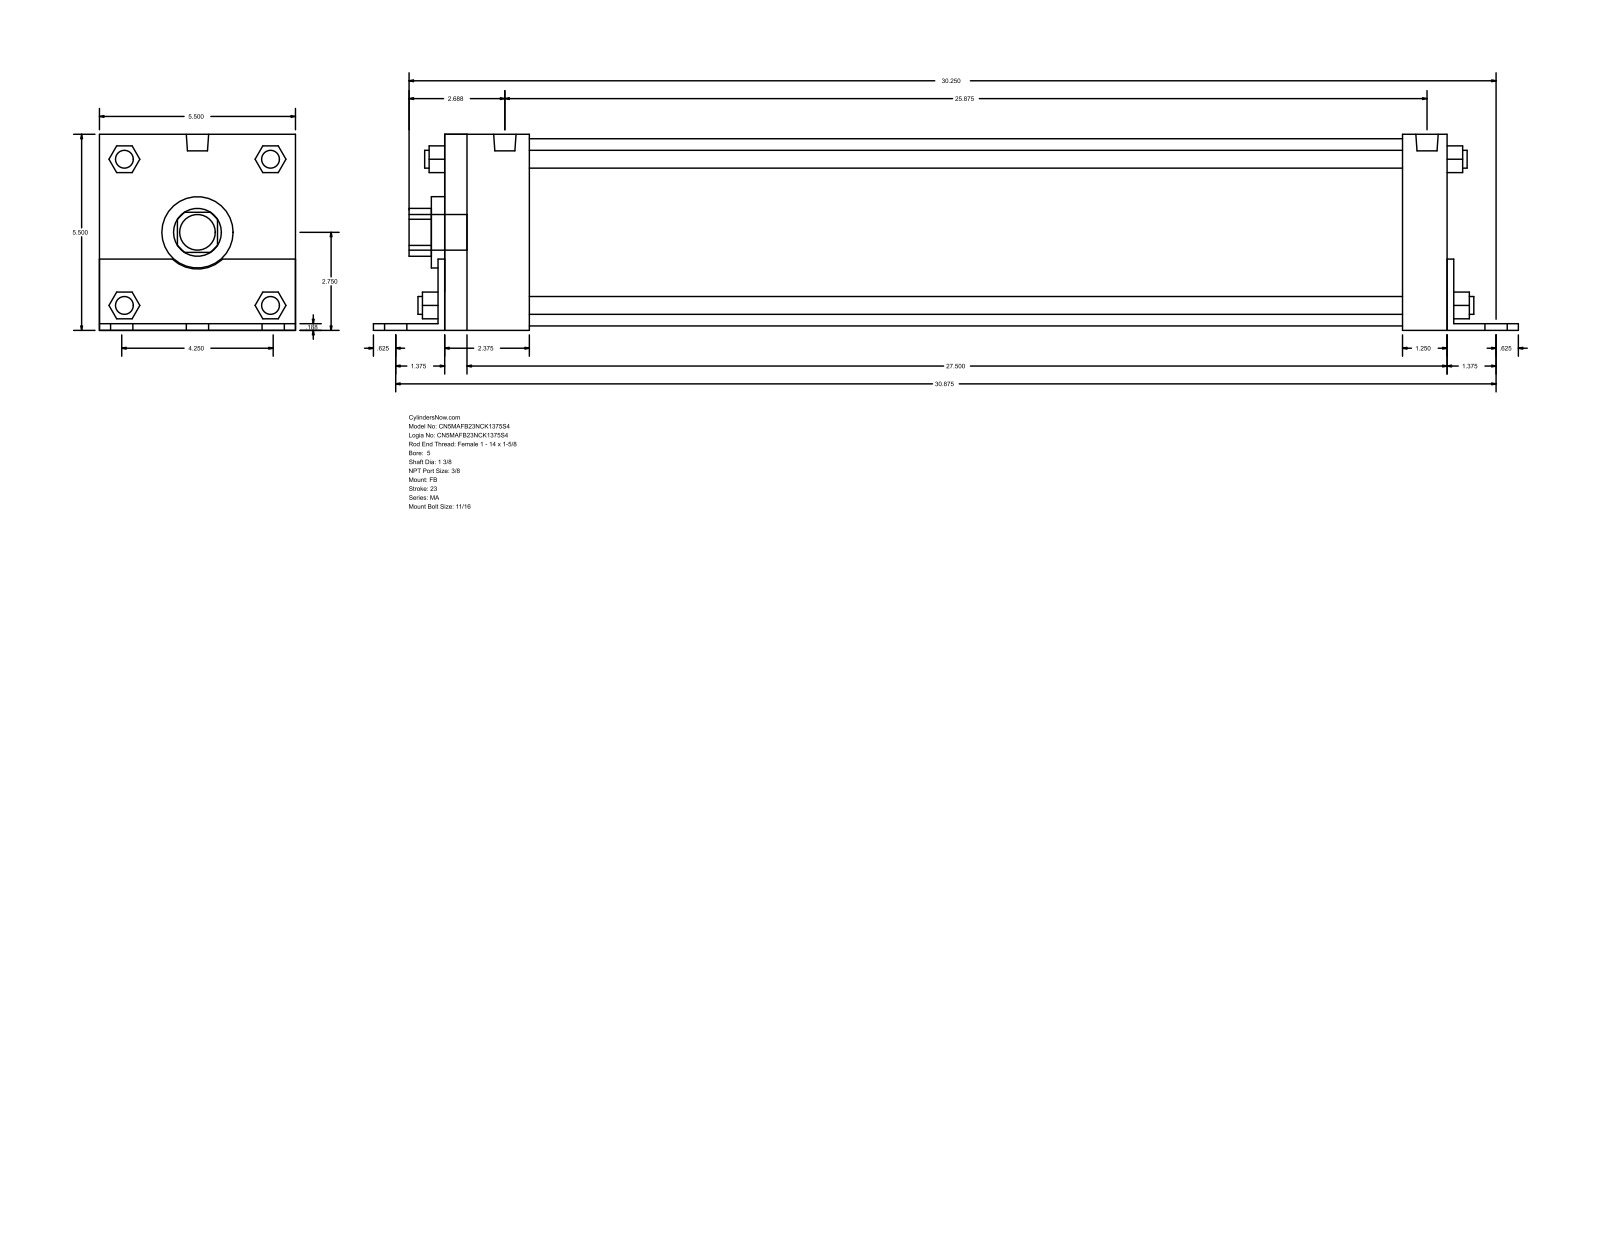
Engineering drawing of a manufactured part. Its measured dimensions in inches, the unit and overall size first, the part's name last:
Units: inches
Overall size (bounding box): 32.125 × 5.502 × 5.5
Round holes (diameter × count): ⌀1.375 ×1, ⌀2 ×1, ⌀5.25 ×1
Round bosses / shafts (diameter × count): ⌀0.687 ×6, ⌀0.5 ×4, ⌀0.437 ×4, ⌀0.627 ×2, ⌀1 ×1
Partial cylindrical surfaces — rounded edges, fillets, slot ends (radius × count): R0.672 ×1, R1.03 ×1
Main face-to-face distances: 5.5, 0.187, 5.502, 0.185, 5.315, 28.125, 0.188, 28.313, 28.312, 28.5
Bodies: 0 solids, 140 faces (105 planar, 35 cylindrical, 0 other)
Part name (STEP PRODUCT): MA_FB__0500_1.375
STEP written by: GSSL Pune (CONFIG_CONTROL_DESIGN)
